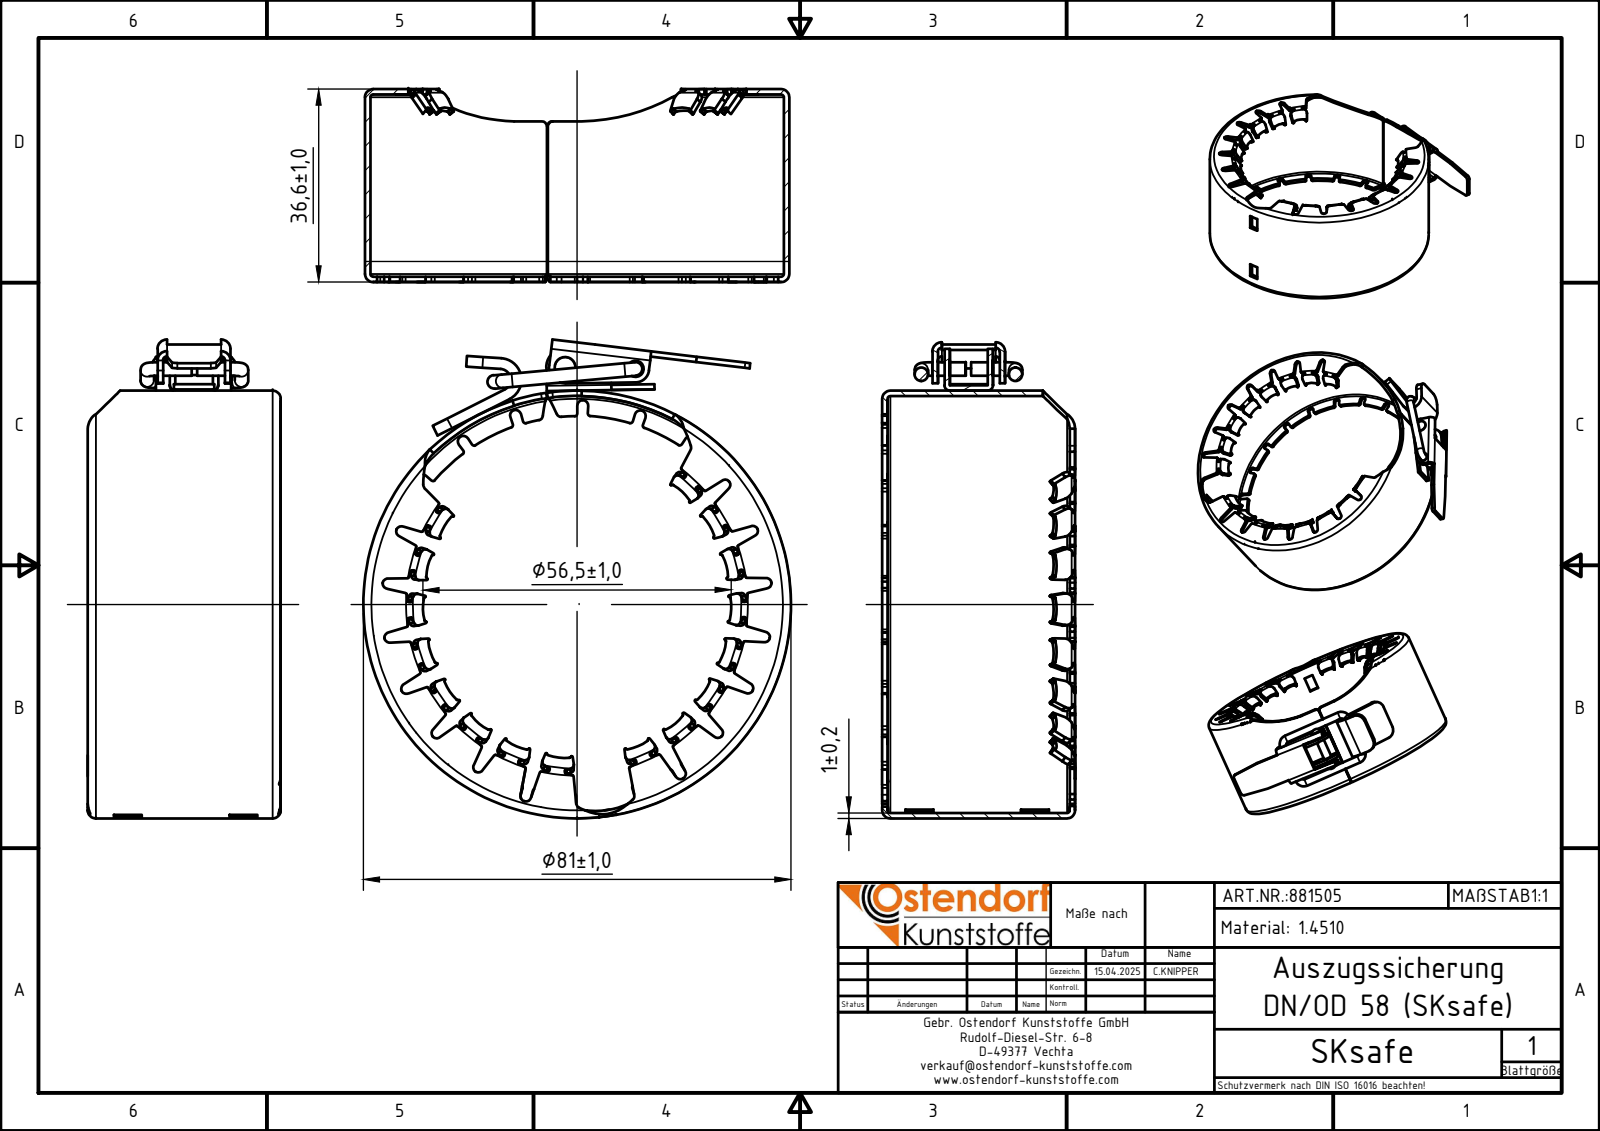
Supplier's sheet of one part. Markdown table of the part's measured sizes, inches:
| quantity | value |
| --- | --- |
| part name | 881505z |
| STEP written by | Autodesk Inventor 2024 (AUTOMOTIVE_DESIGN) |
| units | inches |
| bodies | 6 solids, 1034 faces (104 planar, 89 cylindrical, 841 other) |
| overall size | 3.5 × 3.126 × 1.41 |
| volume | 0.76 in³ |
| surface area | 39.33 in² |
| round holes (diameter × count) | 0.118 × 3, 3.047 × 1 |
| round bosses / shafts (diameter × count) | 0.098 × 3, 3.126 × 1, 0.11 × 1 |
| partial cylindrical surfaces (radius × count) | 0.083 × 13, 0.118 × 5, 0.039 × 4, 0.029 × 2, 0.069 × 2, 0.083 × 2, 0.138 × 2, 0.079 × 1 |
| main face-to-face distances | 0.039, 0.079, 0.491, 0.315, 0.087, 0.404, 0.402, 0.089, 0.368, 0.456 |
| hole center spacings | 0.197, 0.317, 0.514, 1.731, 1.736, 1.774 |
